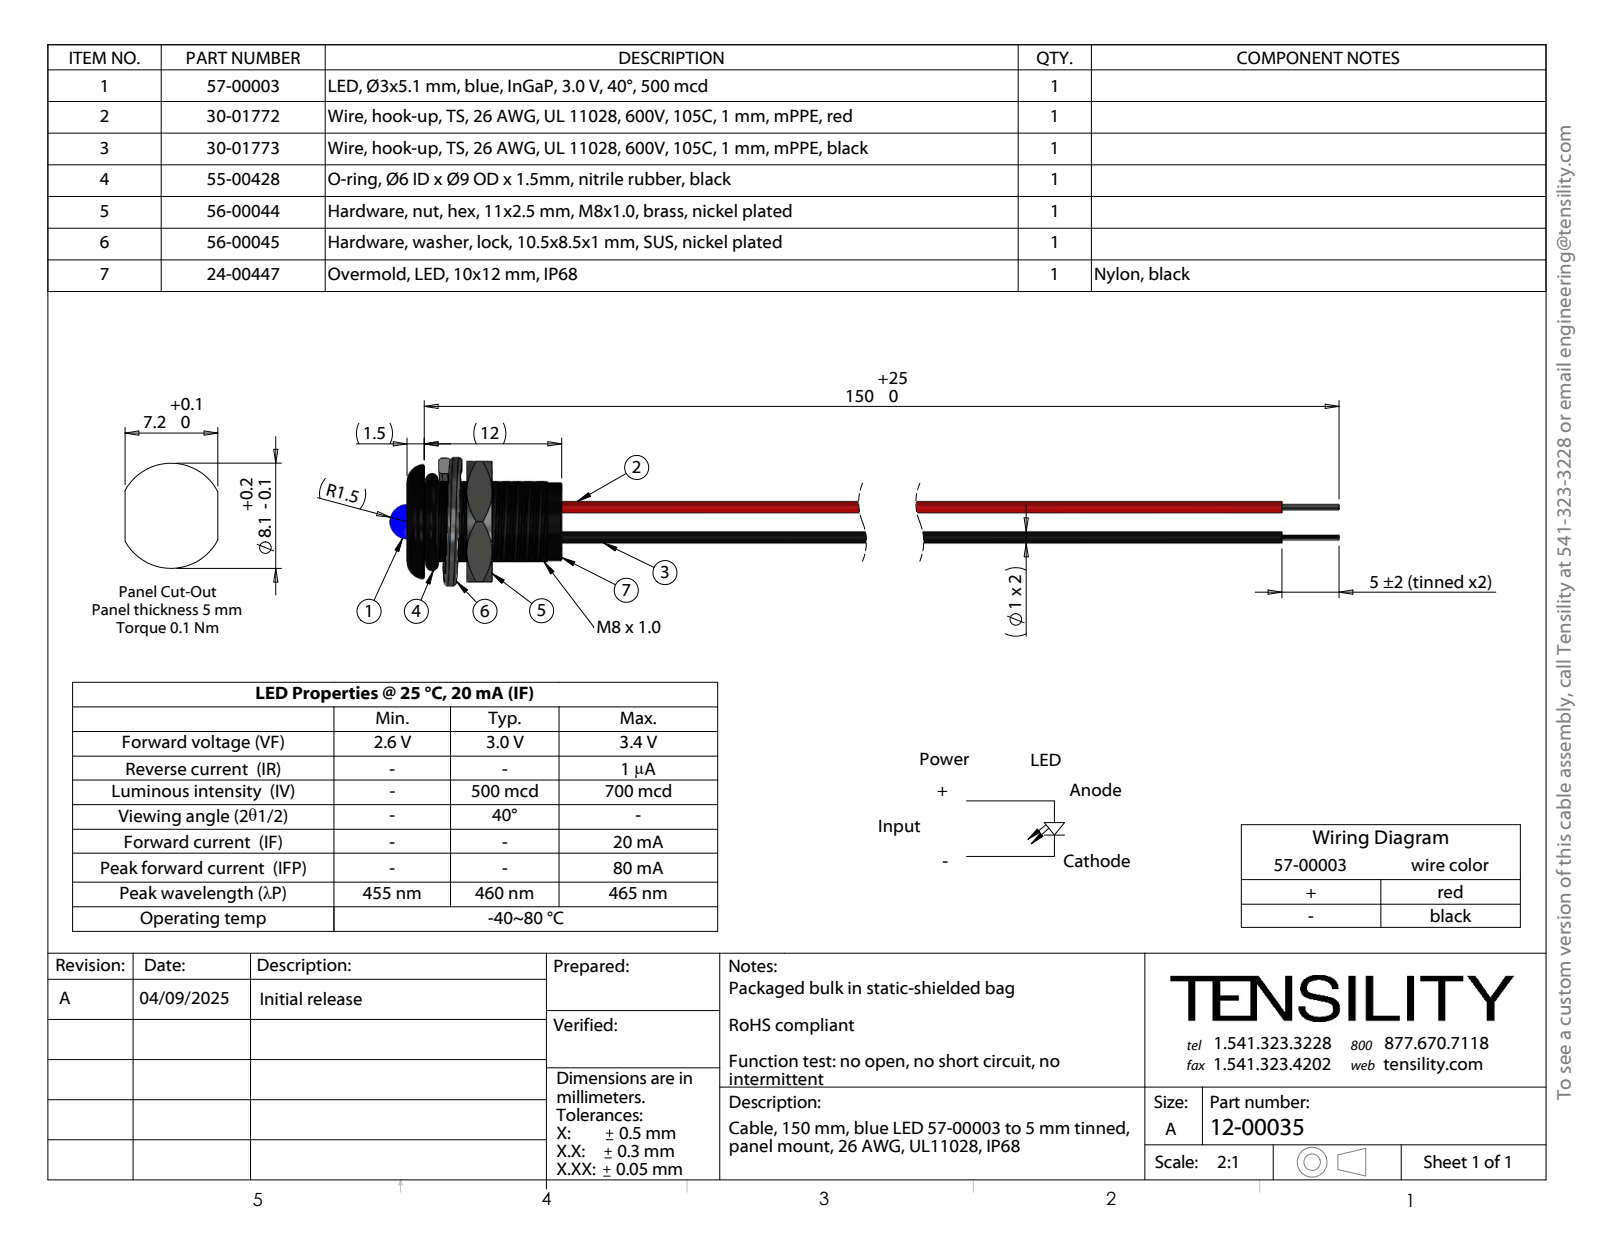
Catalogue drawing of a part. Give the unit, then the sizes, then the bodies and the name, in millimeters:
Units: millimetres
Overall size (bounding box): 169.99 × 12.12 × 11.21
Round holes (diameter × count): ⌀1 ×2
Round bosses / shafts (diameter × count): ⌀1 ×2, ⌀0.5 ×2, ⌀6.8 ×1, ⌀3 ×1
Partial cylindrical surfaces — rounded edges, fillets, slot ends (radius × count): R3.48 ×1, R4 ×1
Main face-to-face distances: 1.5, 13.5, 12, 10.5, 5.21, 3.71, 8.29, 7.41, 5.91, 2.2
Hole centre spacings: 0.36, 0.38, 0.33, 2.48, 2.52, 2.43, 2.44, 2.56
Volume: 1 005 mm³ · Surface area: 5 908 mm²
Bodies: 57 solids, 555 faces (186 planar, 246 cylindrical, 123 other)
Part name (STEP PRODUCT): 56-00044; 24-00447; 56-00045_Split washer; 55-00428 (+4 more)
STEP written by: SolidWorks 2021 (CONFIG_CONTROL_DESIGN)
